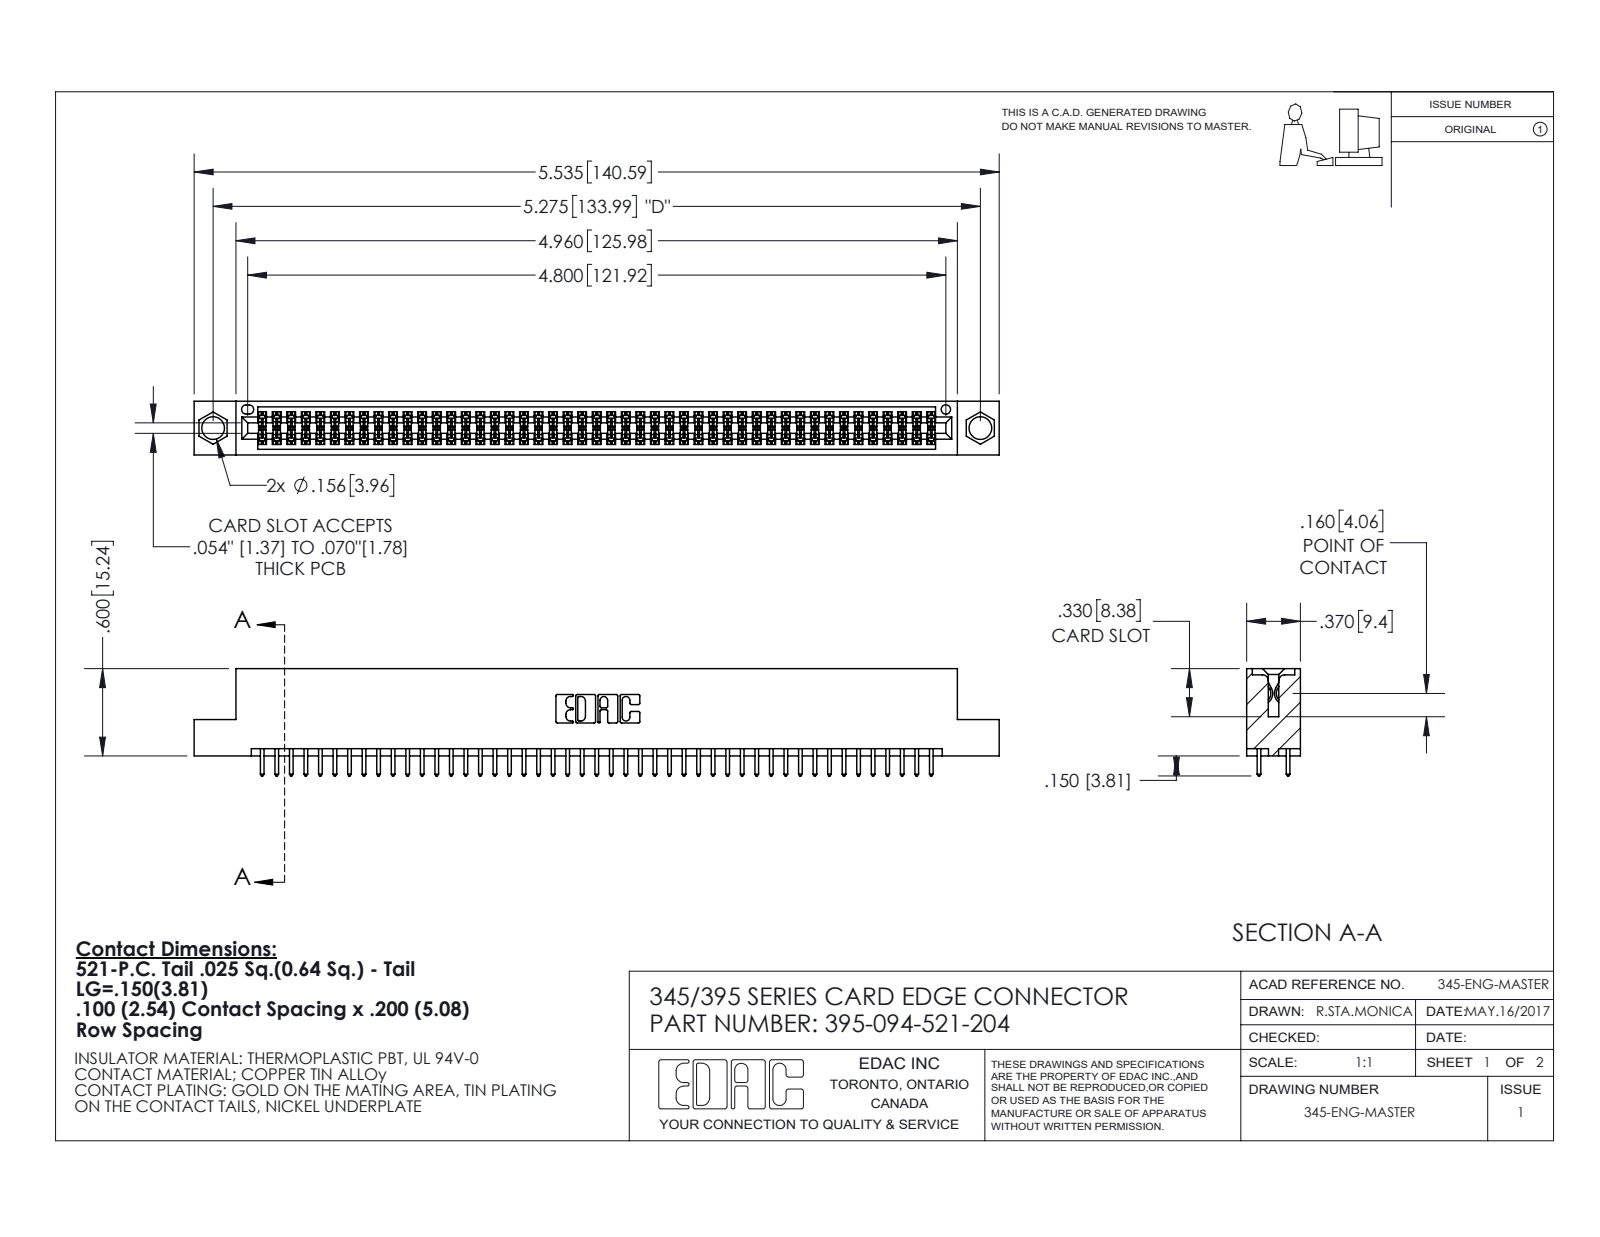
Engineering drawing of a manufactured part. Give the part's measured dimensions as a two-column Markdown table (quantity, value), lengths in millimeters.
| quantity | value |
| --- | --- |
| part name | 395-094-521-204; 345 Part_Flush Mounting Lugs - 0.156 Dia-TI; 345-292-001_345-293-121 |
| STEP written by | SolidWorks 2020 (CONFIG_CONTROL_DESIGN) |
| units | millimeters |
| bodies | 95 solids, 4840 faces (3196 planar, 1644 cylindrical, 0 other) |
| overall size | 140.6 × 18.7 × 9.4 |
| volume | 13 600 mm³ |
| surface area | 19 740 mm² |
| round holes (diameter × count) | 4 × 2, 1.6 × 1 |
| partial cylindrical surfaces (radius × count) | 0.2 × 188, 0.3 × 94, 0.3 × 22, 0.2 × 6, 0.8 × 6, 0.7 × 3, 0.4 × 2, 0.5 × 2 |
| main face-to-face distances | 1.8, 7.6, 5.1, 9.4, 2.5, 6.9, 0.6, 5.7, 4.4, 3.8 |
| hole center spacings | 6.9, 128, 134 |
